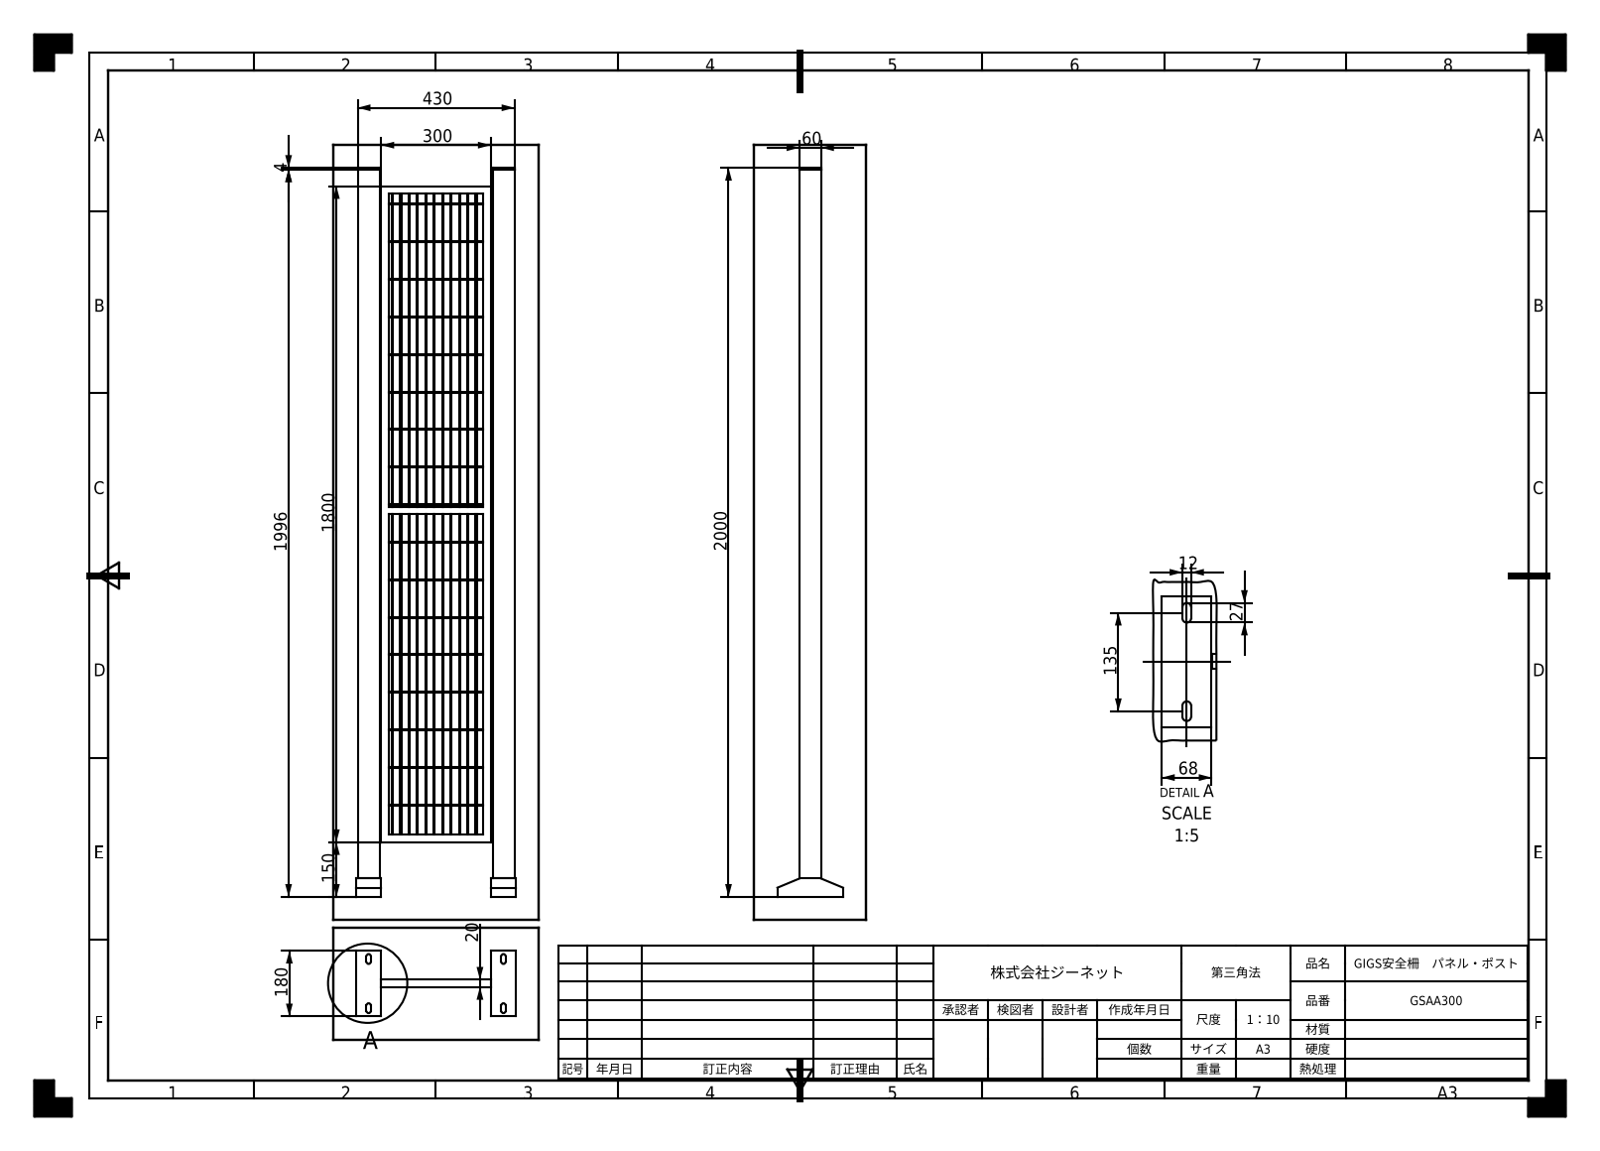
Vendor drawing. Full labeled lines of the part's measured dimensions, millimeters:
Part name (STEP PRODUCT): post_3; GSAA300_1; GSAA300_202104
STEP written by: SIEMENS PLM Software NX 12.0 (AUTOMOTIVE_DESIGN)
Units: millimetres
Bodies: 33 solids, 156 faces (118 planar, 38 cylindrical, 0 other)
Overall size (bounding box): 2000 × 438 × 180
Volume: 16 980 000 mm³ · Surface area: 1 626 000 mm²
Round bosses / shafts (diameter × count): ⌀3 ×28
Partial cylindrical surfaces — rounded edges, fillets, slot ends (radius × count): R6 ×8
Main face-to-face distances: 60, 370, 20, 430, 310, 39.37, 20.63, 19.37, 40.63, 65
